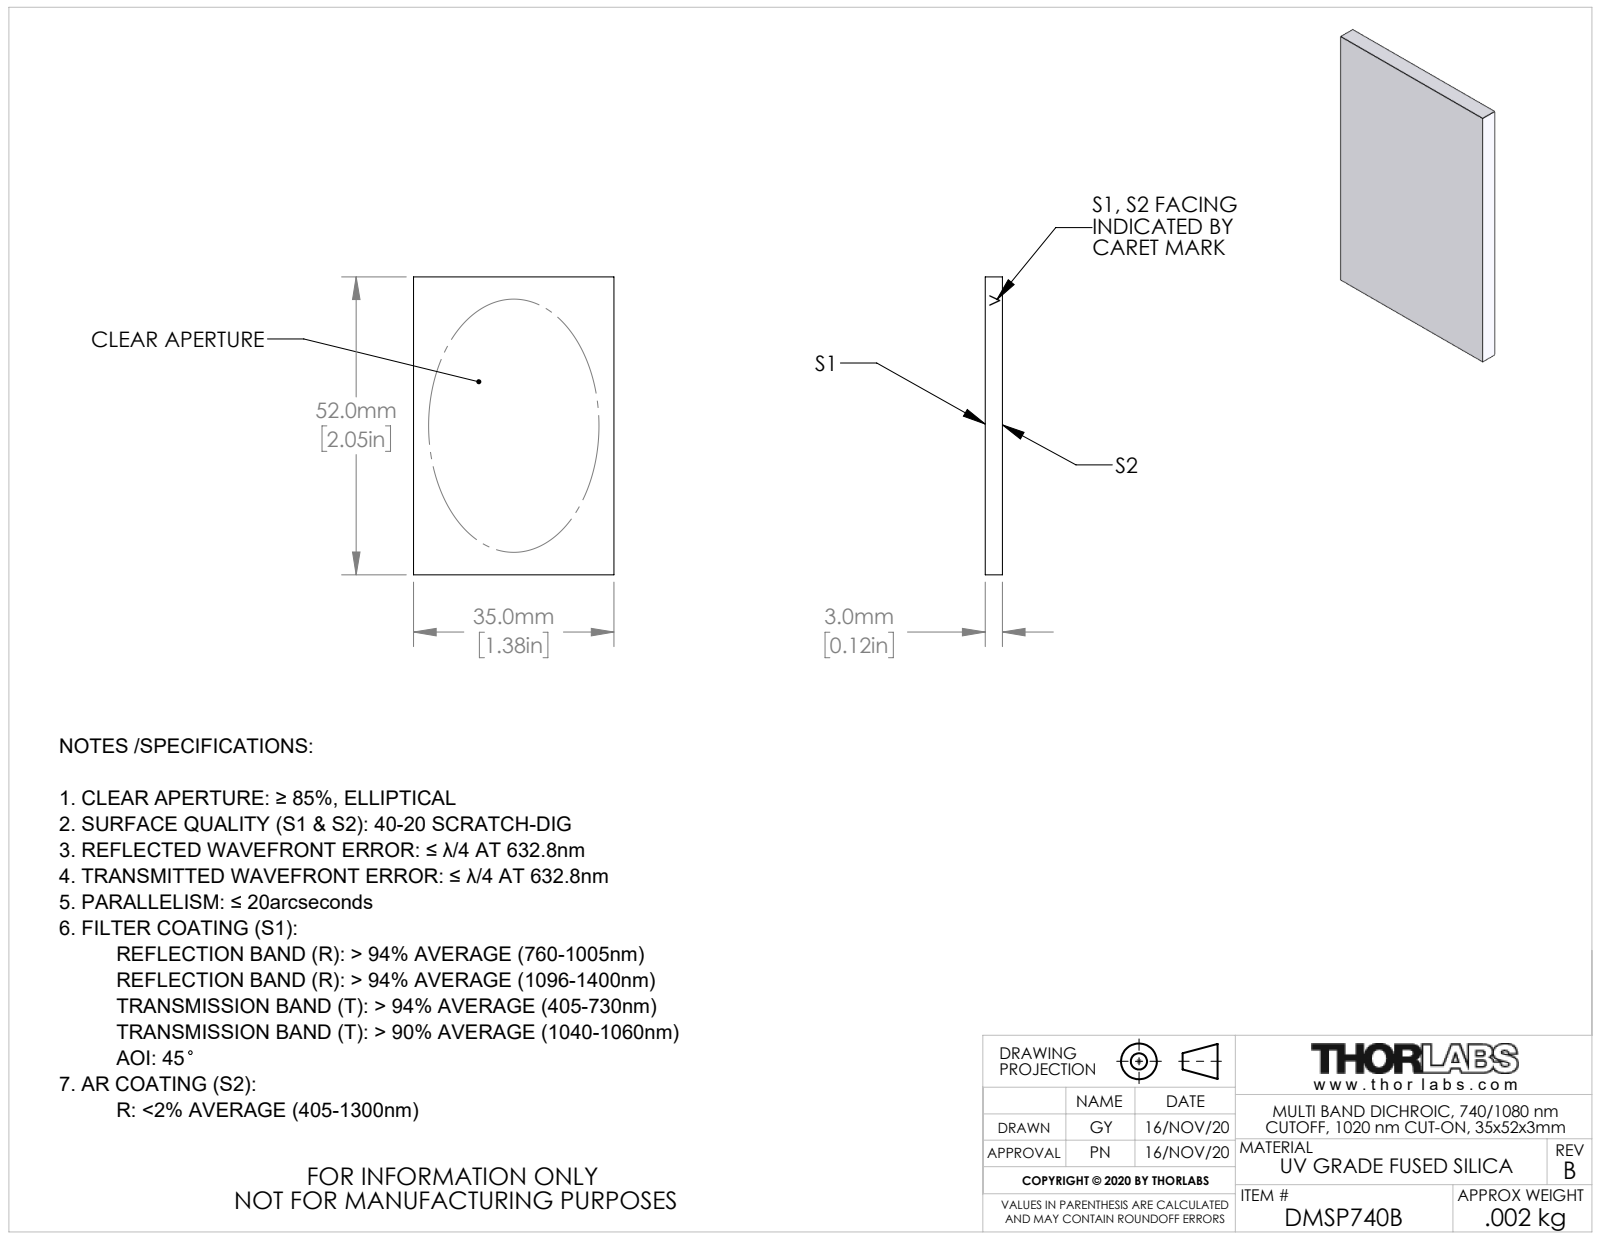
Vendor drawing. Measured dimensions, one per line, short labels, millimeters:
name: TTN166720-E0W
written by: SolidWorks 2018 (AUTOMOTIVE_DESIGN)
unit: mm
bodies: 1 solid, 6 faces (6 planar, 0 cylindrical, 0 other)
size: 52 × 35 × 3
volume: 5 460 mm³; area: 4 162 mm²
face distances: 3, 35, 52
